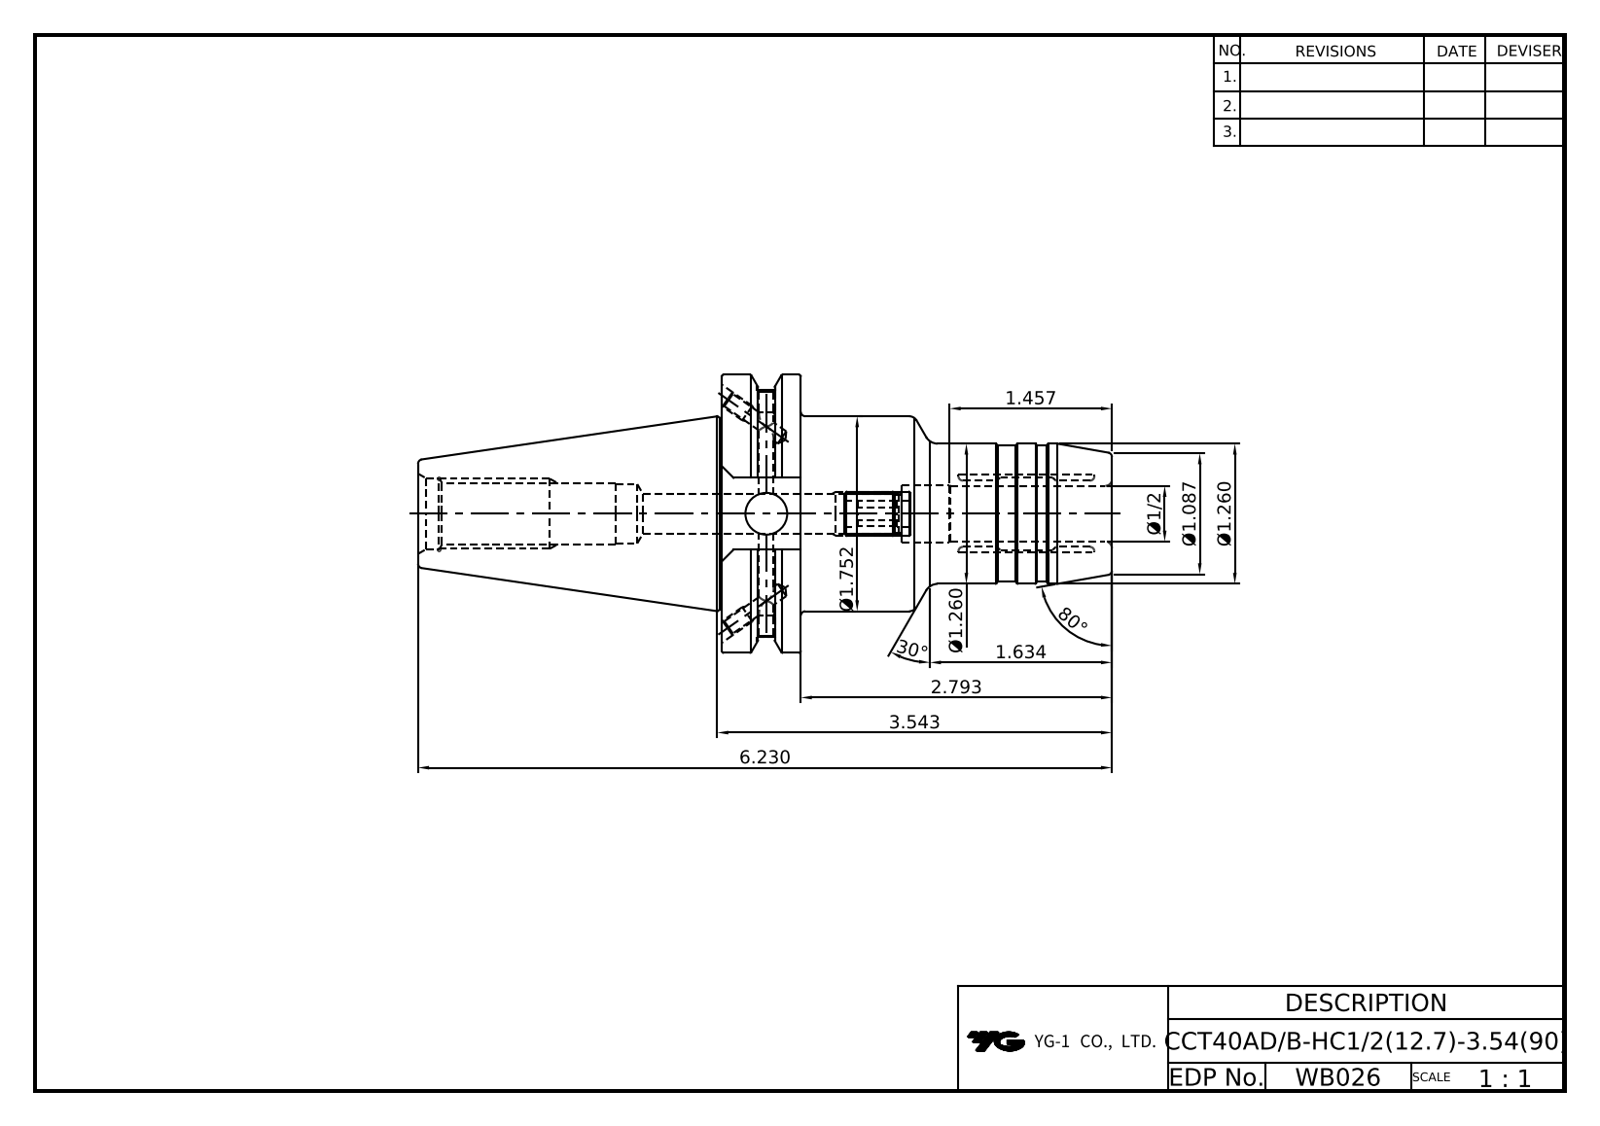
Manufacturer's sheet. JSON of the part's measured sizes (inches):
{"part_name": "LO-CCT40ADB-HC12.7-90", "step_written_by": "Autodesk Inventor 2022 (AUTOMOTIVE_DESIGN)", "units": "inches", "bodies": {"solids": 1, "faces": 106, "planar": 34, "cylindrical": 34, "other": 38}, "overall_size": [6.23, 2.5, 2.405], "volume_in3": 10.67, "surface_area_in2": 47.62, "round_holes": [[0.128, 4], [0.157, 2], [0.165, 2], [0.351, 1], [0.375, 1], [0.5, 1], [0.512, 1], [0.52, 1], [0.527, 1], [0.642, 1]], "round_bosses_or_shafts": [[2.5, 1], [1.752, 1], [1.724, 1], [1.26, 1], [1.22, 1]], "partial_cylinders_radius": [[1.108, 1]], "face_to_face_distances": [0.711, 3.504, 2.793, 1.874, 0.645, 2.726, 3.437, 6.23, 3.202, 0.476]}
